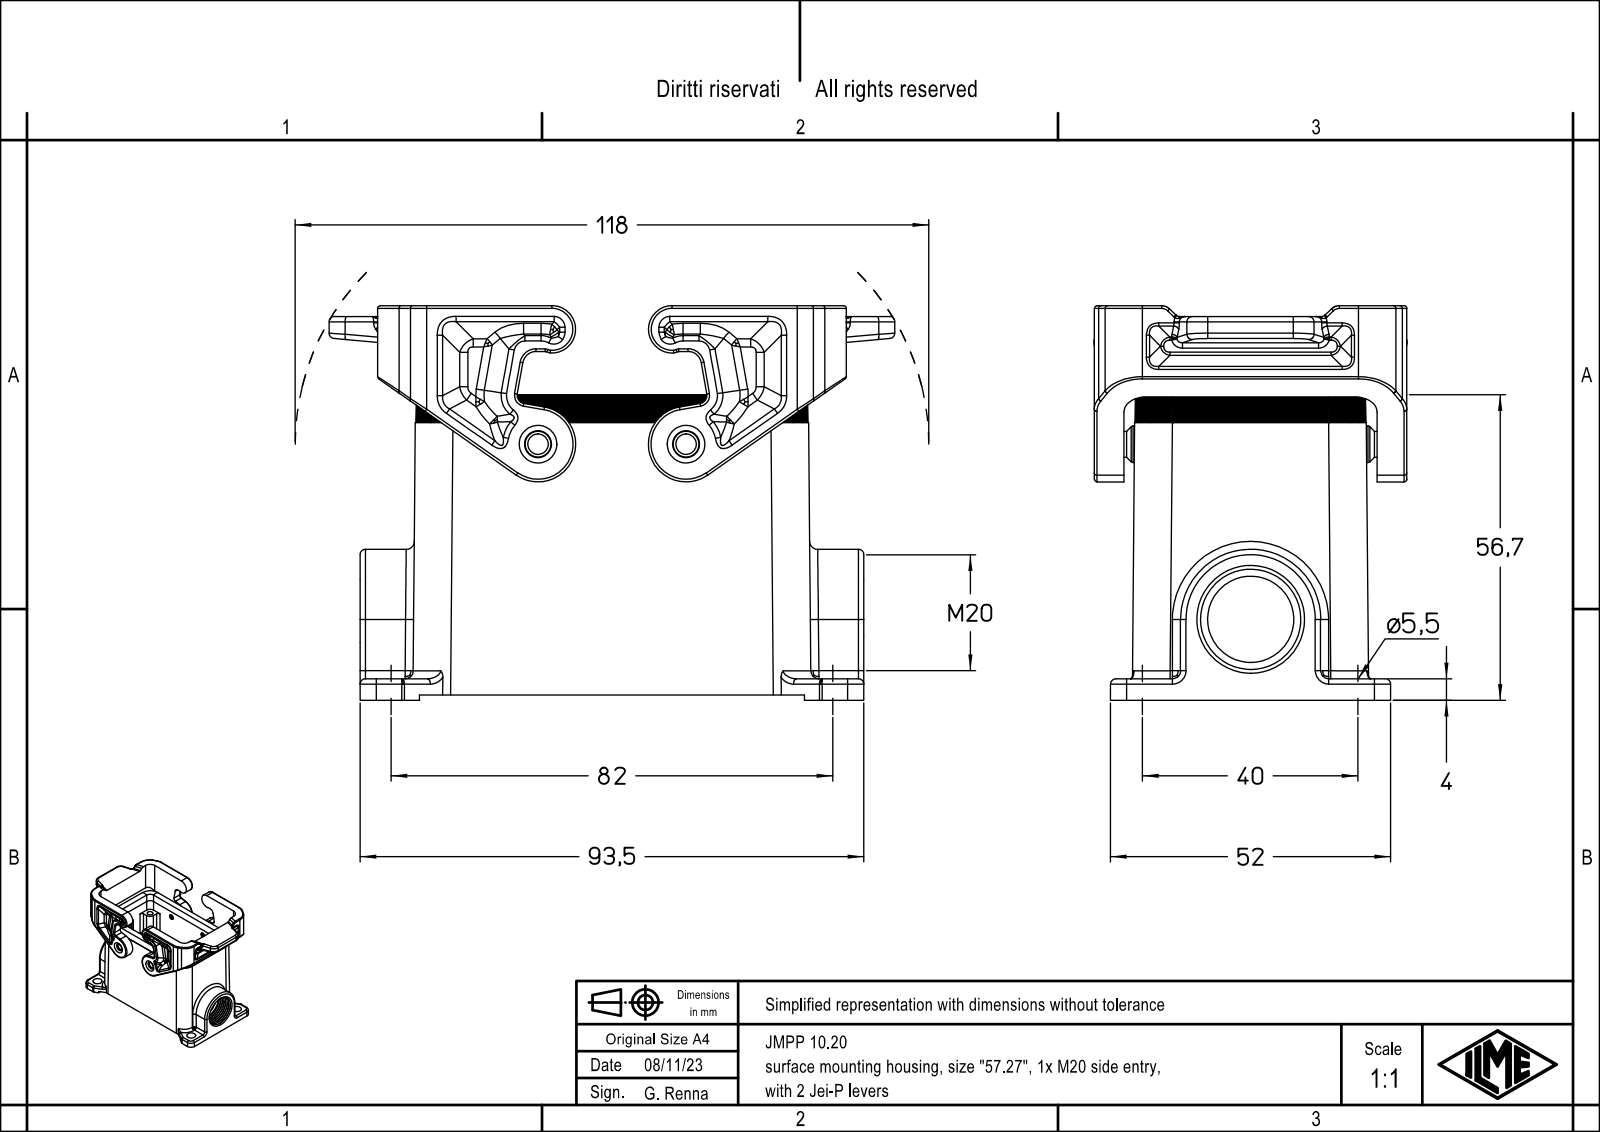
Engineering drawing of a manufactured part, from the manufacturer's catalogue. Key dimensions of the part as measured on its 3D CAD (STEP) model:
Part name (STEP PRODUCT): JMPP 10.20
STEP written by: Creo Elements/Direct Modeling 20.1B 02-Apr-2019 (C) Parametric Technology GmbH (AUTOMOTIVE_DESIGN)
Units: millimetres
Bodies: 1 solid, 890 faces (172 planar, 320 cylindrical, 398 other)
Overall size (bounding box): 105 × 73.2 × 58.08
Volume: 100 953 mm³ · Surface area: 46 627 mm²
Round holes (diameter × count): ⌀3 ×4, ⌀3.5 ×4, ⌀5.5 ×4, ⌀4.8 ×2, ⌀16 ×1, ⌀18.6 ×1
Round bosses / shafts (diameter × count): ⌀6.8 ×2
Partial cylindrical surfaces — rounded edges, fillets, slot ends (radius × count): R0.5 ×50, R1 ×48, R3 ×38, R2 ×25, R1.5 ×20, R4 ×12, R6 ×12, R7 ×10
Main face-to-face distances: 3, 47, 1, 4, 52.5, 5.5, 72.2, 2, 8.25, 85.25
Hole centre spacings: 14.09, 35.76, 69.8, 77.15, 27, 40, 57, 63.07
